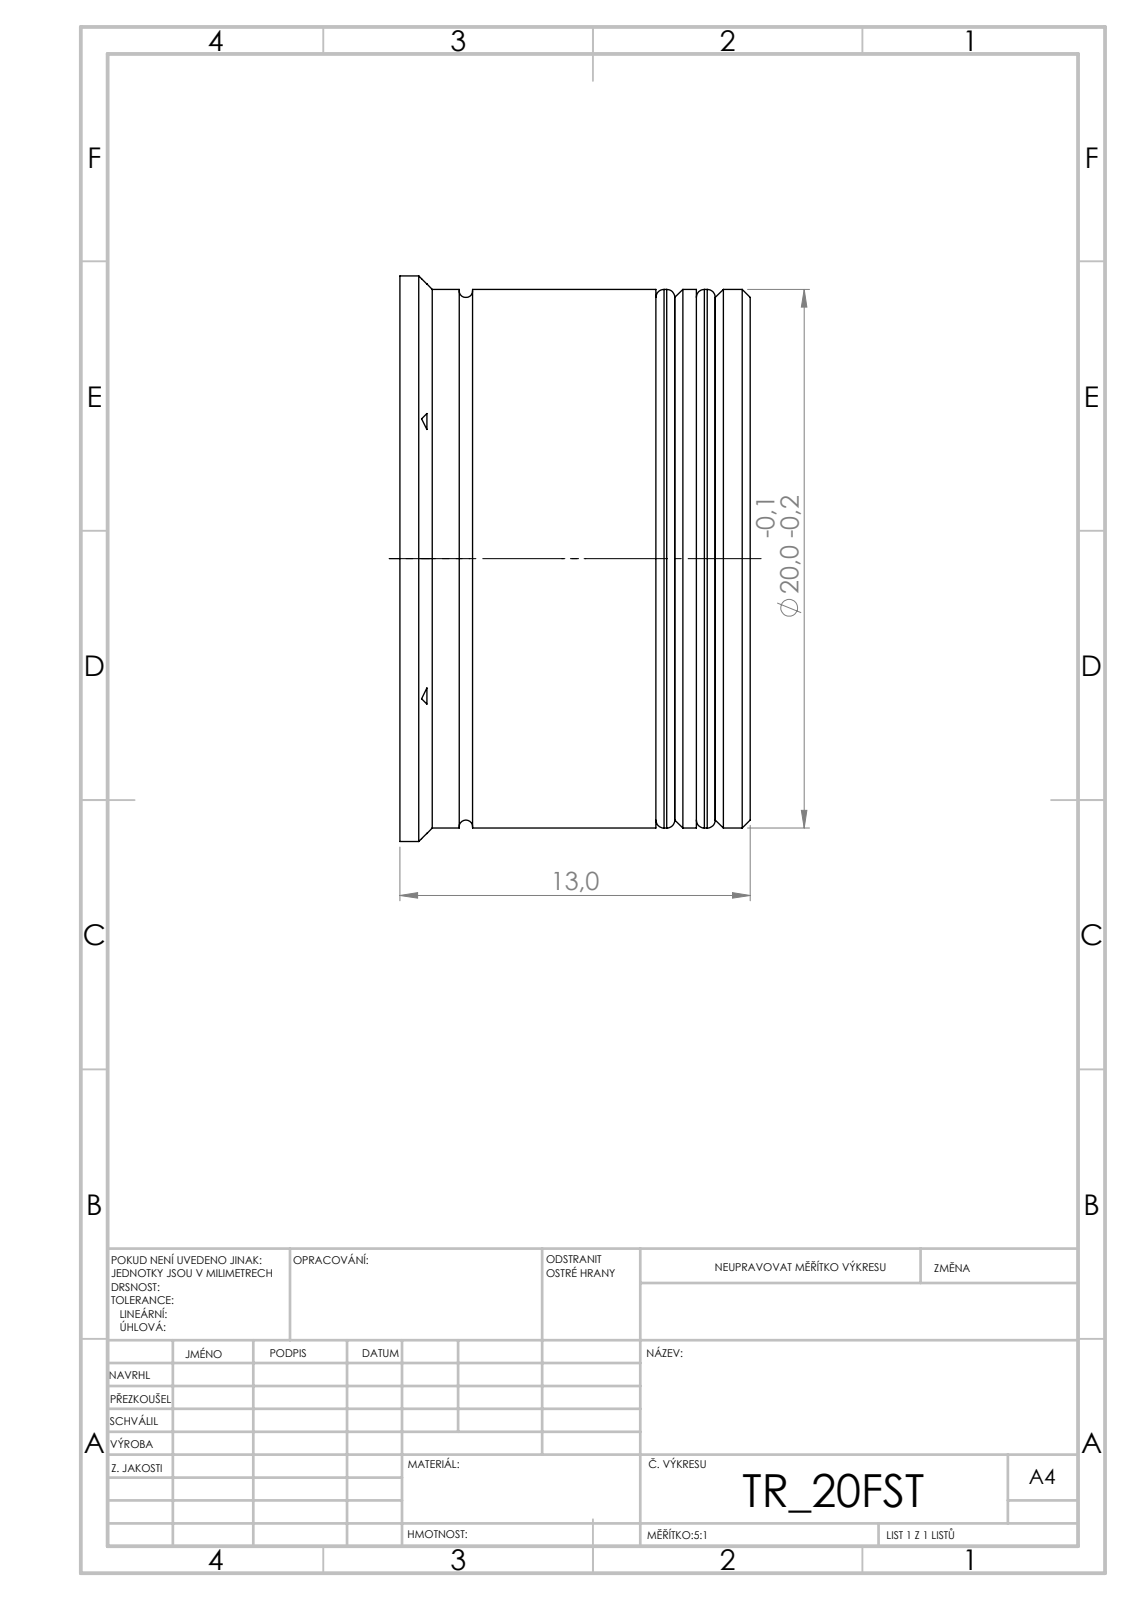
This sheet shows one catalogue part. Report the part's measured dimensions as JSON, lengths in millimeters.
{"step_written_by": "SolidWorks 2019 (CONFIG_CONTROL_DESIGN)", "units": "millimeters", "bodies": {"solids": 3, "faces": 74, "planar": 29, "cylindrical": 25, "other": 20}, "overall_size": [21, 21, 13], "volume_mm3": 4239, "surface_area_mm2": 2998, "round_bosses_or_shafts": [[21, 1], [20, 1], [19.4, 1]], "partial_cylinders_radius": [[8.5, 1]], "face_to_face_distances": [1.5, 0.7, 2.2, 0.8, 1.3, 2, 2.8, 3.5, 12, 10.7]}
